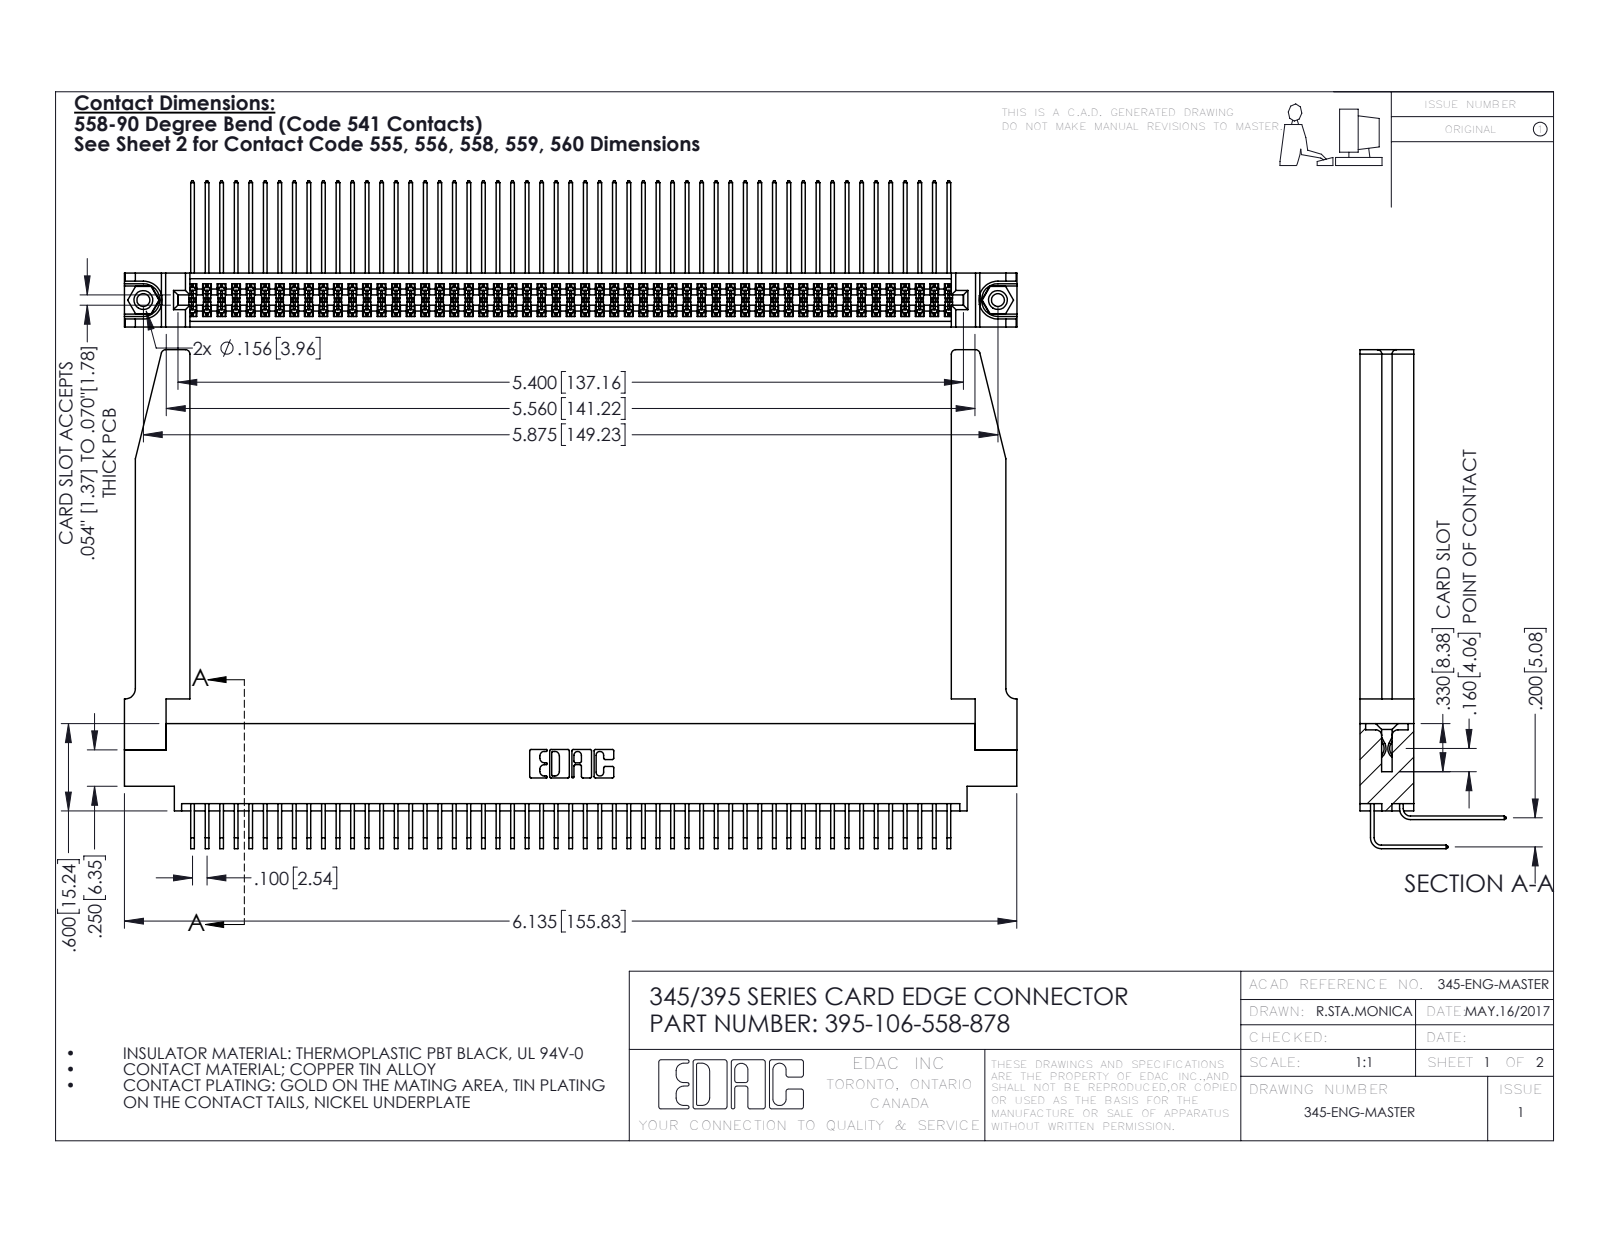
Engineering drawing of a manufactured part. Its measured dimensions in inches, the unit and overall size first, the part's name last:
Units: inches
Overall size (bounding box): 6.136 × 3.429 × 1.005
Round holes (diameter × count): ⌀0.089 ×2, ⌀0.125 ×2, ⌀0.156 ×2, ⌀0.064 ×1
Round bosses / shafts (diameter × count): ⌀0.155 ×2
Partial cylindrical surfaces — rounded edges, fillets, slot ends (radius × count): R0.006 ×160, R0.01 ×22, R0.03 ×8, R0.007 ×6, R0.031 ×6, R0.026 ×3, R0.014 ×2, R0.019 ×2
Main face-to-face distances: 0.072, 0.37, 0.298, 0.2, 0.098, 0.272, 0.025, 0.225, 0.175, 0.025
Hole centre spacings: 0.27, 5.639, 5.875
Volume: 1.435 in³ · Surface area: 51.67 in²
Bodies: 111 solids, 5876 faces (3936 planar, 1888 cylindrical, 52 other)
Part name (STEP PRODUCT): 345-292-001_558 Tail - 2; 345 Part_0.170 Offset - 0.156 Dia-TH; 345-220-078_345-220-078; 345-250-001_345-250-001-102 (+2 more)
STEP written by: SolidWorks 2016 (CONFIG_CONTROL_DESIGN)
